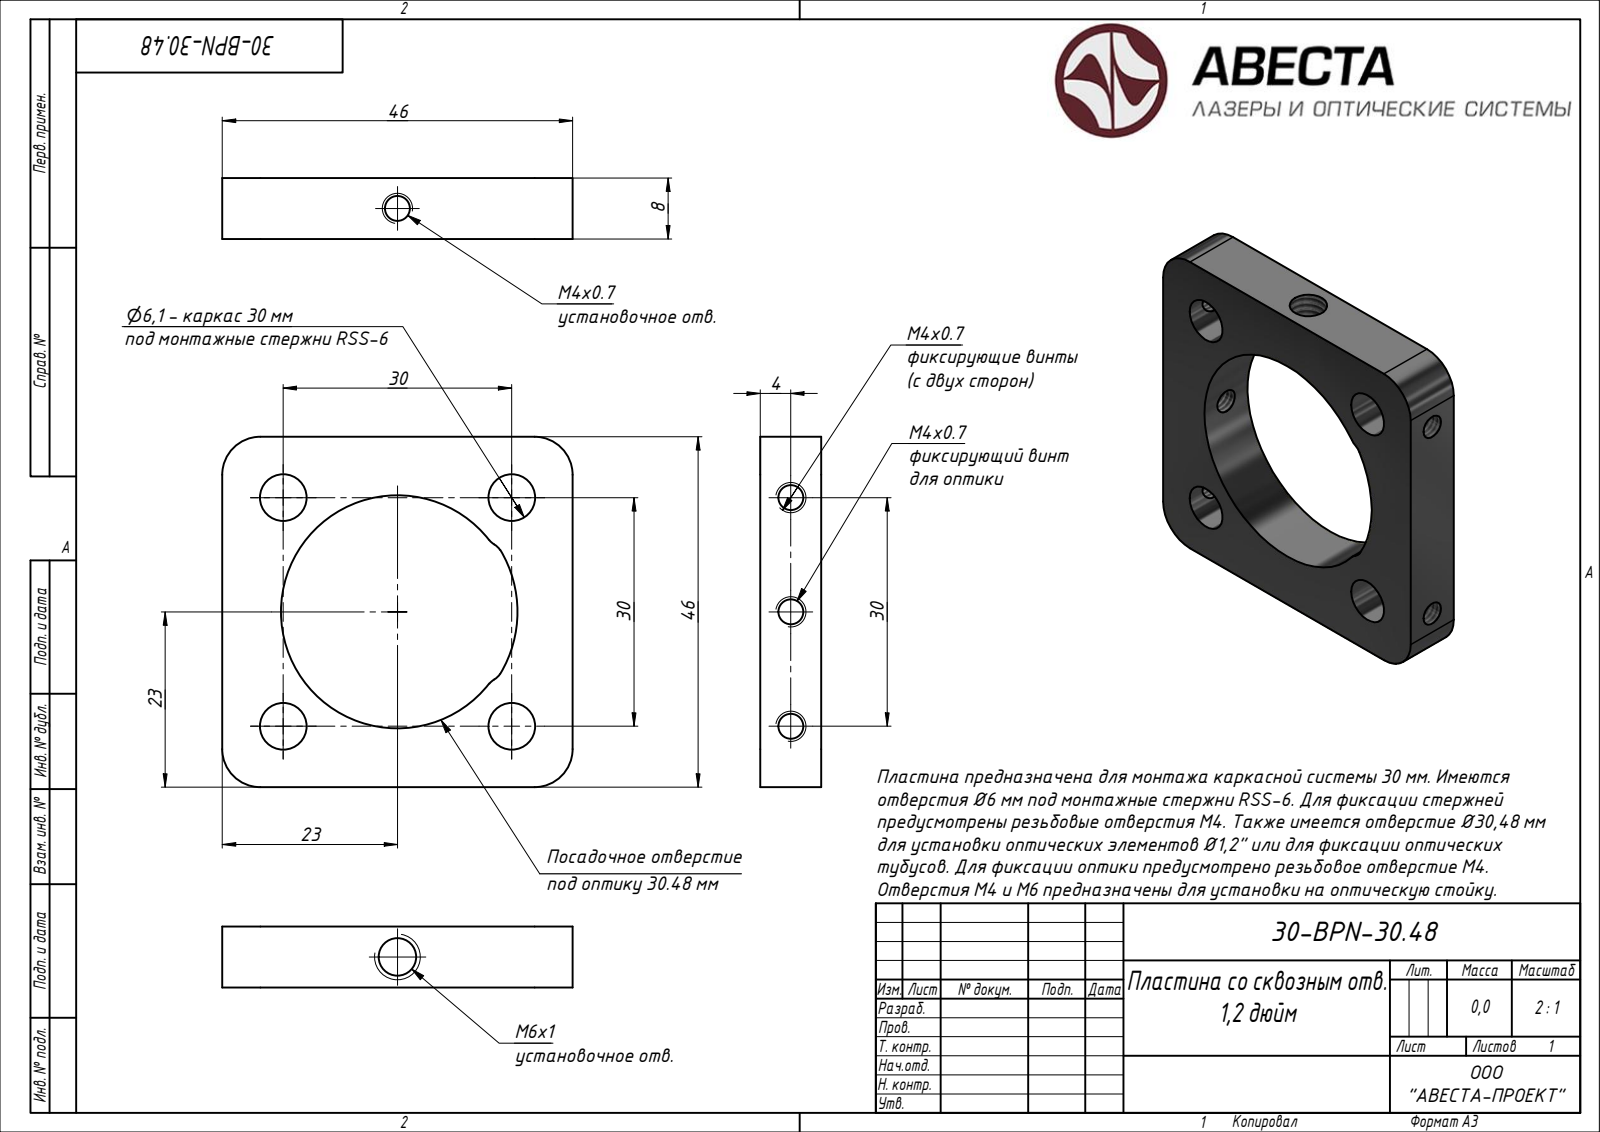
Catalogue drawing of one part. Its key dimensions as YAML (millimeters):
part_name: "30-BPN-30,48"
step_written_by: "Autodesk Inventor 2020 (AUTOMOTIVE_DESIGN)"
units: millimeters
bodies: {solids: 1, faces: 29, planar: 6, cylindrical: 21, other: 2}
overall_size: [46, 46, 8]
volume: 9464
surface_area: 5623
round_holes:
  - {diameter: 3.24, count: 4}
  - {diameter: 6.1, count: 4}
  - {diameter: 4.92, count: 1}
partial_cylinders:
  - {radius: 2, count: 4}
  - {radius: 5, count: 4}
  - {radius: 15.3, count: 1}
  - {radius: 15.75, count: 1}
face_to_face_distances: [8, 46]
hole_center_spacings: [30, 15, 42.43]
